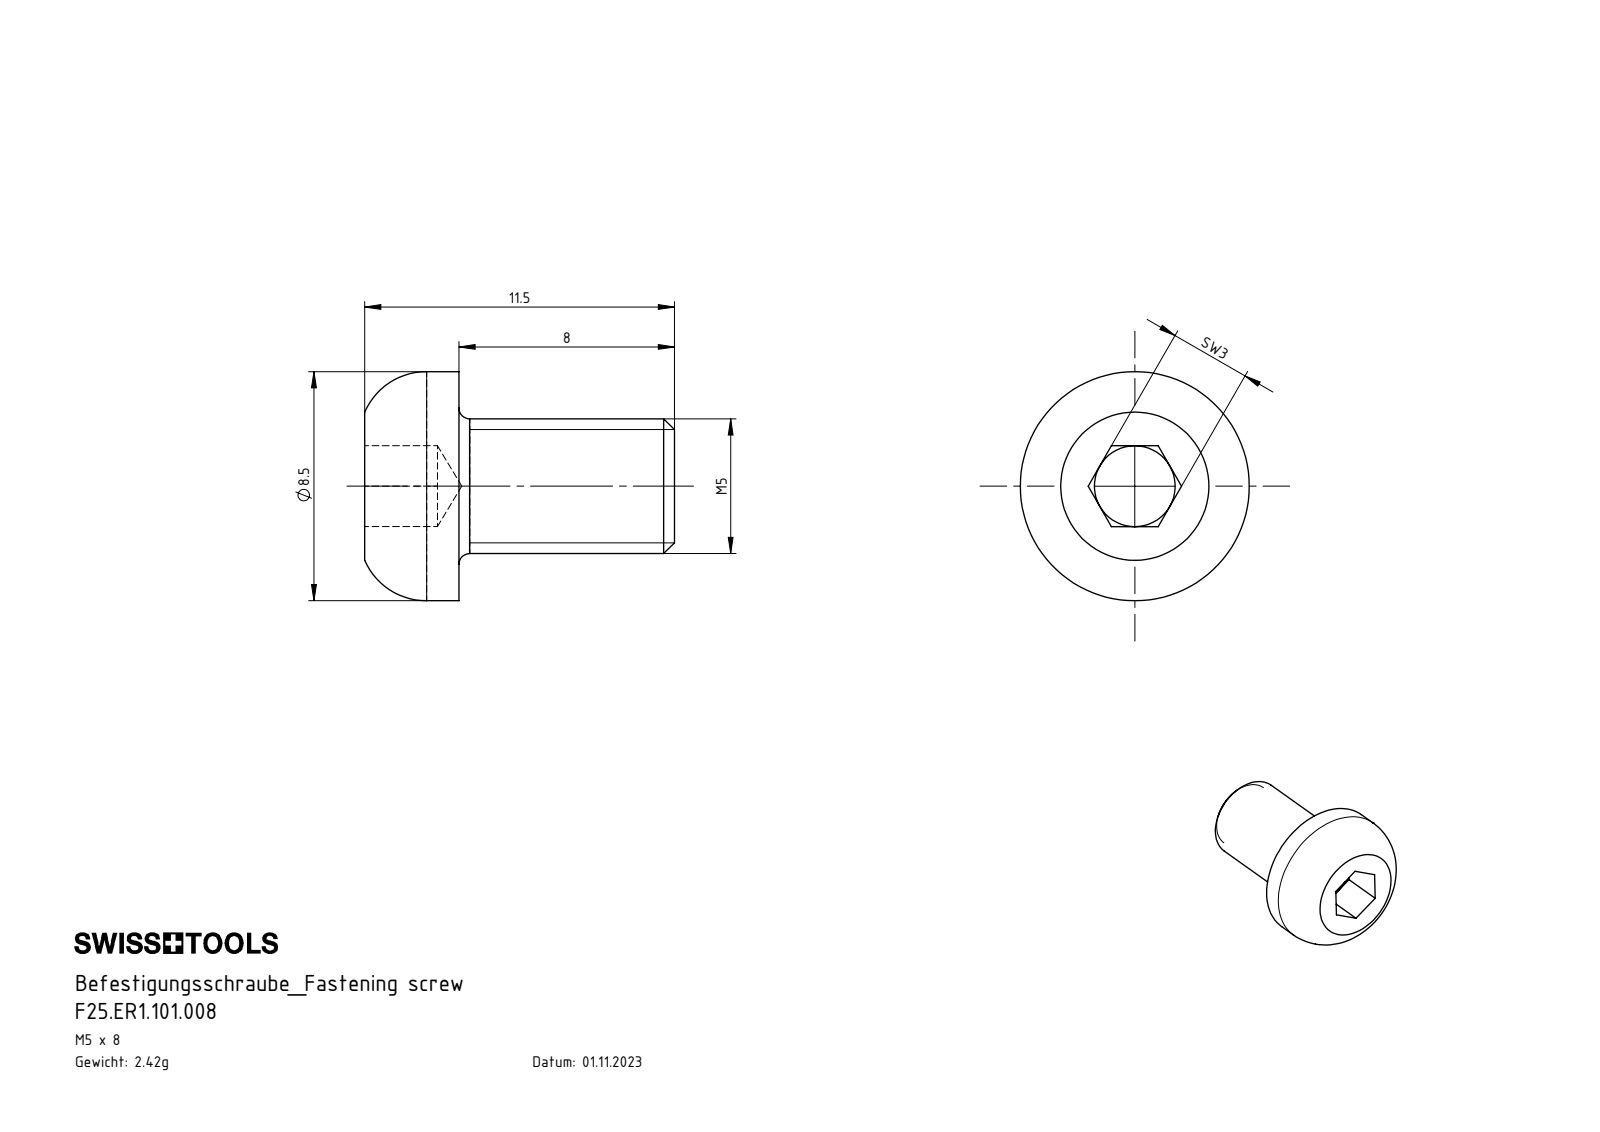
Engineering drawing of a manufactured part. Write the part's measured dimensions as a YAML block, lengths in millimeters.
part_name: "F25.ER1.101.008"
step_written_by: "SolidWorks 2017 (AUTOMOTIVE_DESIGN)"
units: millimeters
bodies: {solids: 1, faces: 27, planar: 15, cylindrical: 4, other: 8}
overall_size: [11.5, 8.5, 8.5]
volume: 309
surface_area: 329
round_bosses_or_shafts:
  - {diameter: 8.5, count: 1}
  - {diameter: 5, count: 1}
face_to_face_distances: [3.5, 3, 11.5, 8, 2.7, 0.8, 8.8]
